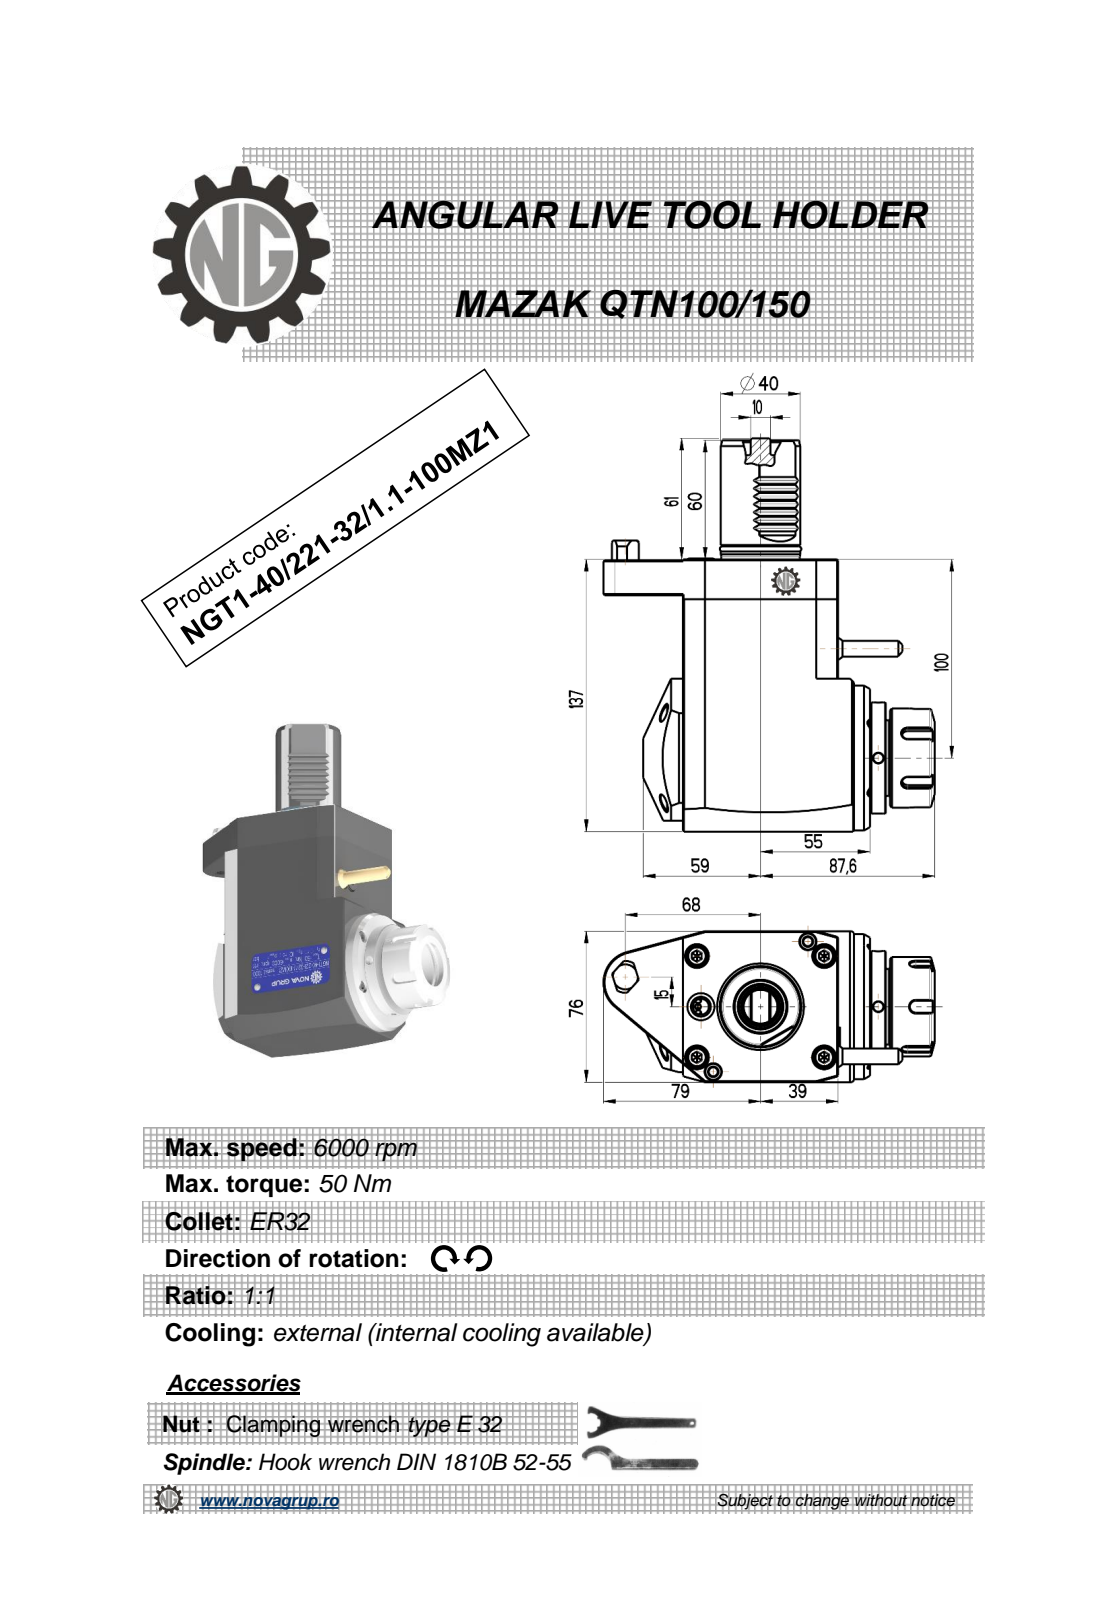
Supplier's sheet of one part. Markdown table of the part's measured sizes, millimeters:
| quantity | value |
| --- | --- |
| part name | NGT1_40_221_32_1_1_100MZ1 |
| STEP written by | PRO/ENGINEER BY PARAMETRIC TECHNOLOGY CORPORATION, 2010280 (CONFIG_CONTROL_DESIGN) |
| units | millimeters |
| bodies | 1 solid, 300 faces (133 planar, 76 cylindrical, 91 other) |
| overall size | 198 × 166.6 × 76 |
| volume | 1 090 000 mm³ |
| surface area | 81 950 mm² |
| round holes (diameter × count) | 5 × 3, 3 × 1, 8 × 1, 26 × 1, 27 × 1 |
| round bosses / shafts (diameter × count) | 73 × 1, 56 × 1, 50 × 1, 43 × 1, 40 × 1, 39.4 × 1, 36.2 × 1, 10 × 1 |
| partial cylindrical surfaces (radius × count) | 0.3 × 7, 0.2 × 6, 3 × 5, 0.8 × 2, 300 × 2, 8 × 1, 9 × 1, 15.84 × 1 |
| main face-to-face distances | 76, 78, 137, 8, 16, 94, 18, 119, 87.92, 7.5 |
| hole center spacings | 30, 59.25, 60.42, 89.25 |
